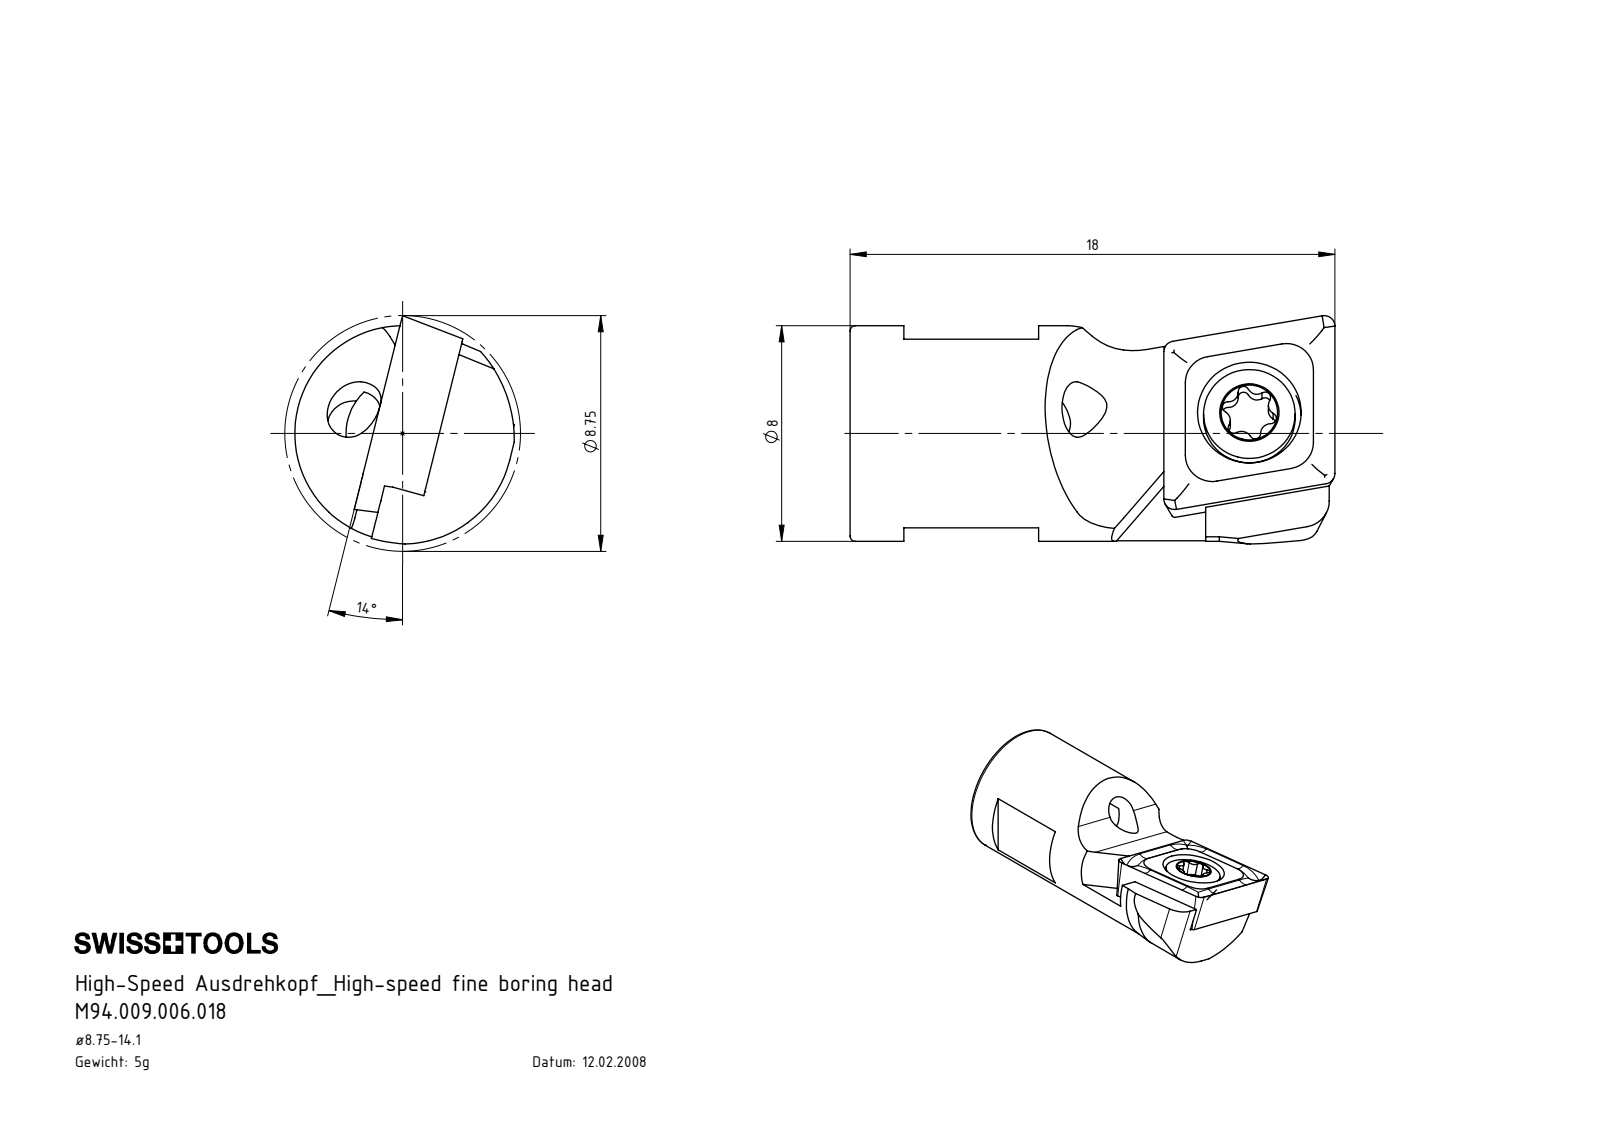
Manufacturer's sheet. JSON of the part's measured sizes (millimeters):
{"part_name": "HS5-A09.K11.018_D; WCA-ER2.001.005_A; CCMT060204; HS5.A09.K11.018", "step_written_by": "SolidWorks 2017 (AUTOMOTIVE_DESIGN)", "units": "millimeters", "bodies": {"solids": 3, "faces": 103, "planar": 40, "cylindrical": 26, "other": 37}, "overall_size": [18, 8.47, 8.15], "volume_mm3": 564, "surface_area_mm2": 796, "round_holes": [[2, 1], [2.05, 1], [2.8, 1], [3.85, 1], [4.2, 1]], "round_bosses_or_shafts": [[8, 1], [3.4, 1], [2.5, 1]], "partial_cylinders_radius": [[0.21, 6], [0.36, 5], [0.36, 1], [1, 1], [2, 1], [3, 1], [4.1, 1], [4.9, 1]], "face_to_face_distances": [7, 2.38, 2.28, 1.5, 0.78, 0.88, 11.8, 5, 4.8, 2]}
